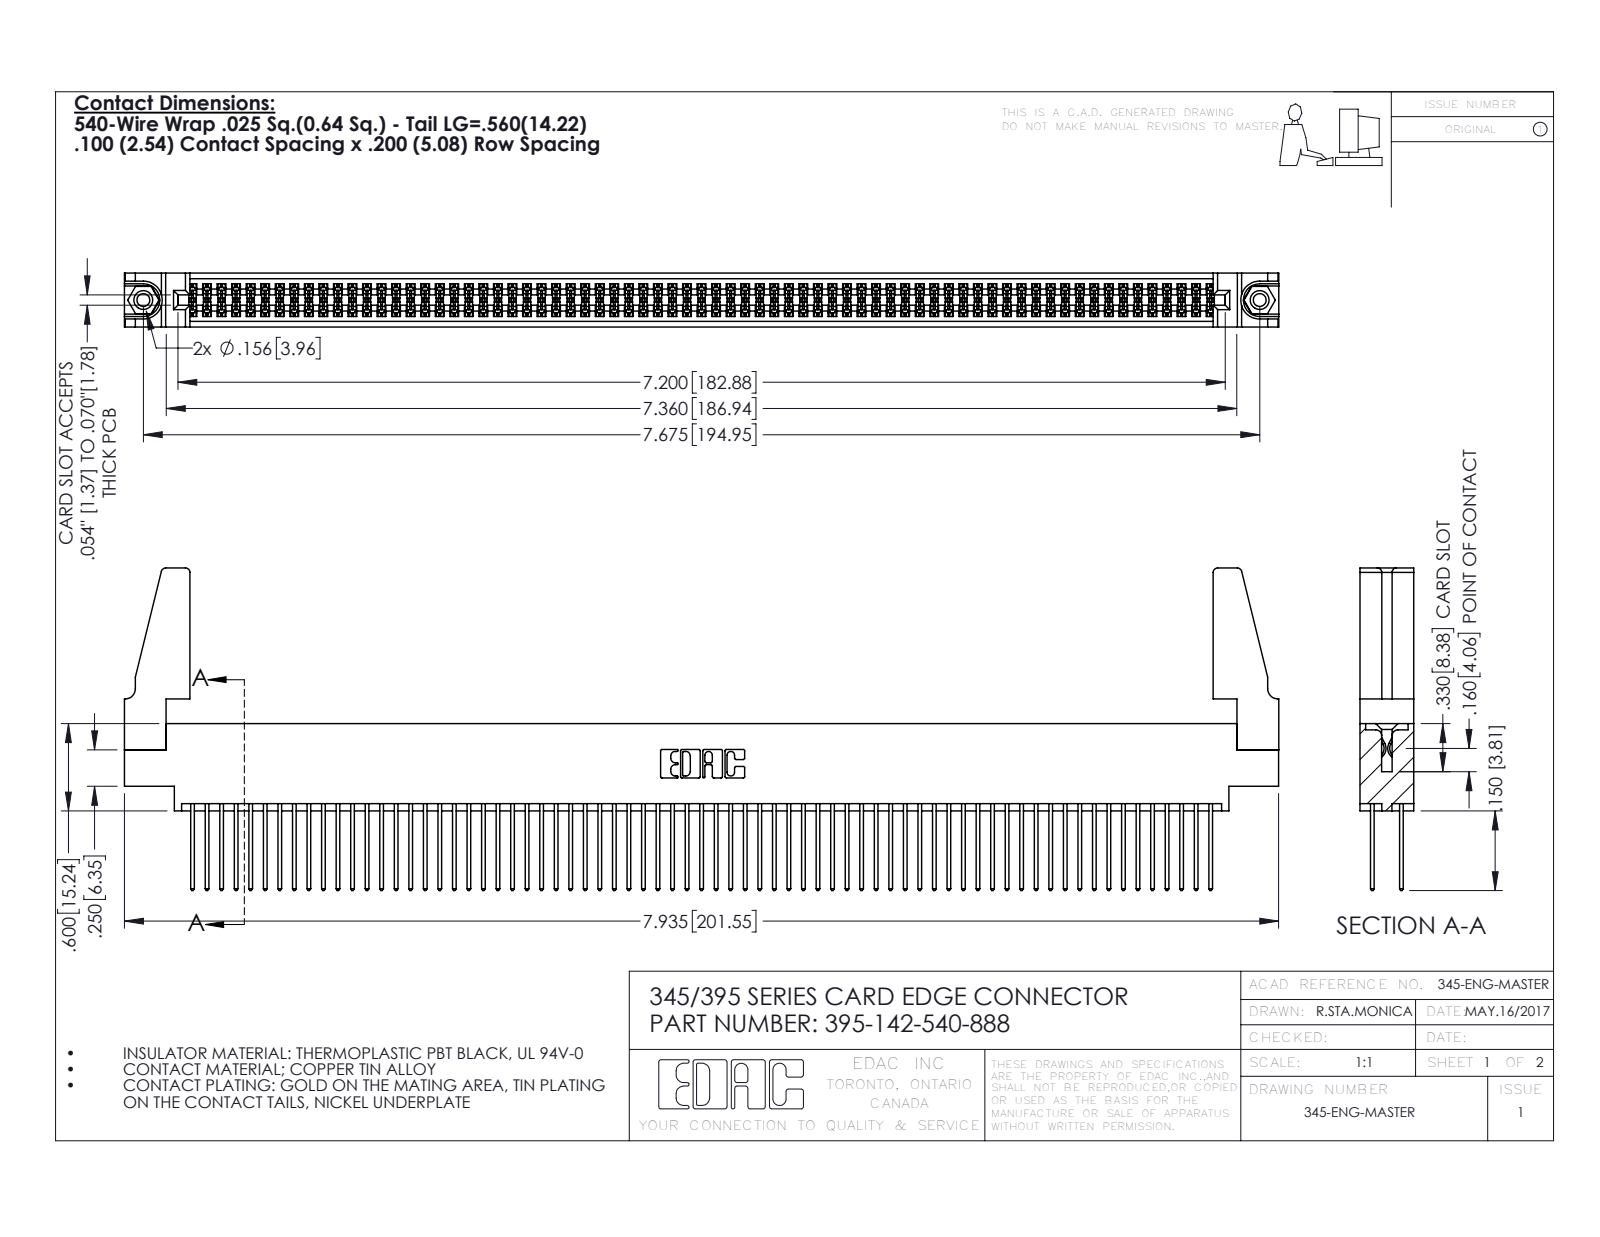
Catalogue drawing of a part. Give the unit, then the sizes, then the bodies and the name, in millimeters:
Units: millimetres
Overall size (bounding box): 201.6 × 56.3 × 9.4
Round holes (diameter × count): ⌀2.3 ×2, ⌀3.2 ×2, ⌀4 ×2, ⌀1.6 ×1
Round bosses / shafts (diameter × count): ⌀3.9 ×2
Partial cylindrical surfaces — rounded edges, fillets, slot ends (radius × count): R0.2 ×213, R0.3 ×142, R0.3 ×22, R0.8 ×8, R0.2 ×6, R0.8 ×6, R0.7 ×3, R0.4 ×2
Main face-to-face distances: 1.8, 7.6, 2.5, 6.9, 0.6, 5.1, 9.4, 5.7, 4.4, 3.8
Hole centre spacings: 6.9, 189, 194.9
Volume: 23 530 mm³ · Surface area: 36 300 mm²
Bodies: 147 solids, 7354 faces (4842 planar, 2496 cylindrical, 16 other)
Part name (STEP PRODUCT): 345-250-001_345-250-001-102; 345 Part_0.170 Offset - 0.156 Dia-TH; 345-292-001_345-293-140; 345-220-078_345-220-088 (+1 more)
STEP written by: SolidWorks 2016 (CONFIG_CONTROL_DESIGN)
